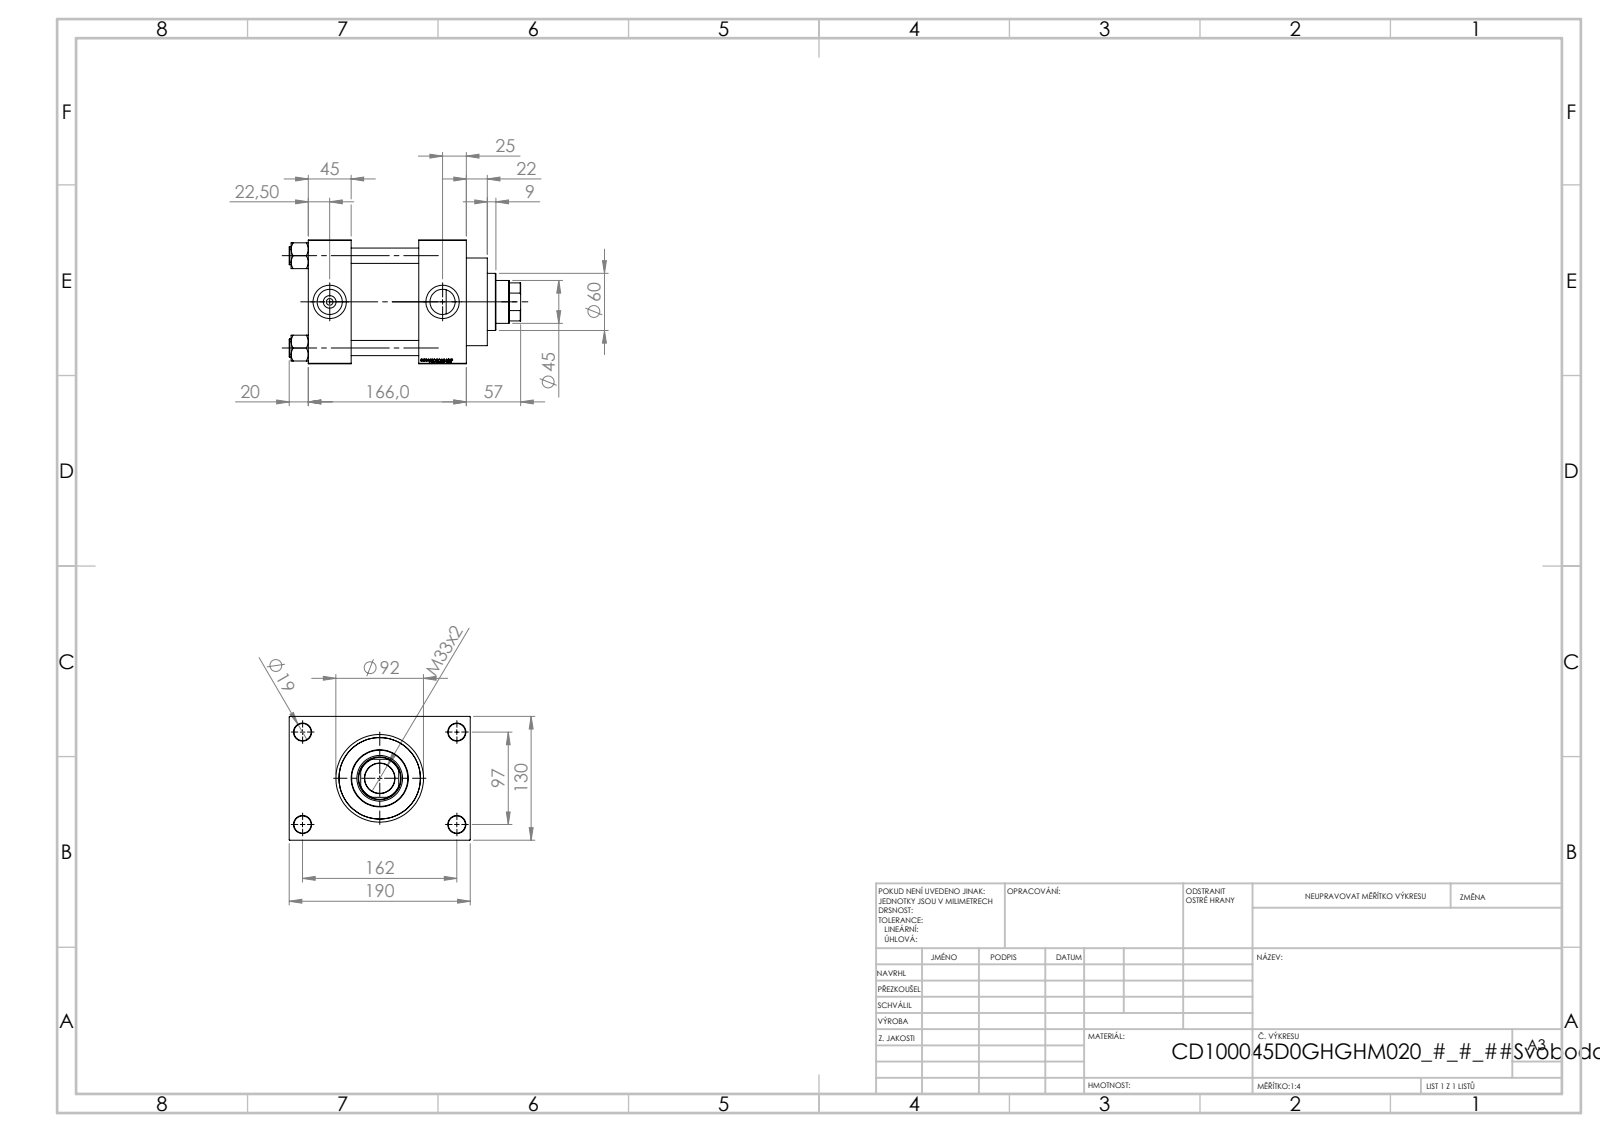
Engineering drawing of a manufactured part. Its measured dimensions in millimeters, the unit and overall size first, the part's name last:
Units: millimetres
Overall size (bounding box): 243 × 190 × 130
Round holes (diameter × count): ⌀16 ×4, ⌀18 ×4, ⌀7 ×2, ⌀26.44 ×2, ⌀35 ×2, ⌀31.5 ×1, ⌀45 ×1, ⌀48 ×1, ⌀76 ×1, ⌀85.5 ×1, ⌀100 ×1
Round bosses / shafts (diameter × count): ⌀19 ×4, ⌀106 ×1, ⌀92 ×1, ⌀60 ×1
Partial cylindrical surfaces — rounded edges, fillets, slot ends (radius × count): R22 ×1
Main face-to-face distances: 130, 45, 116, 71, 166, 121, 50, 30, 160, 20
Hole centre spacings: 32.55, 68.52, 94.41, 96.9, 102.27, 129.45, 161.73, 97
Volume: 896 991 mm³ · Surface area: 354 859 mm²
Bodies: 10 solids, 1151 faces (545 planar, 88 cylindrical, 518 other)
Part name (STEP PRODUCT): V215CD_VCP_D; V215CD_D_TYCINKA; V215CD_VC_A; V215CD_D_Body (+1 more)
STEP written by: SolidWorks 2019 (CONFIG_CONTROL_DESIGN)
